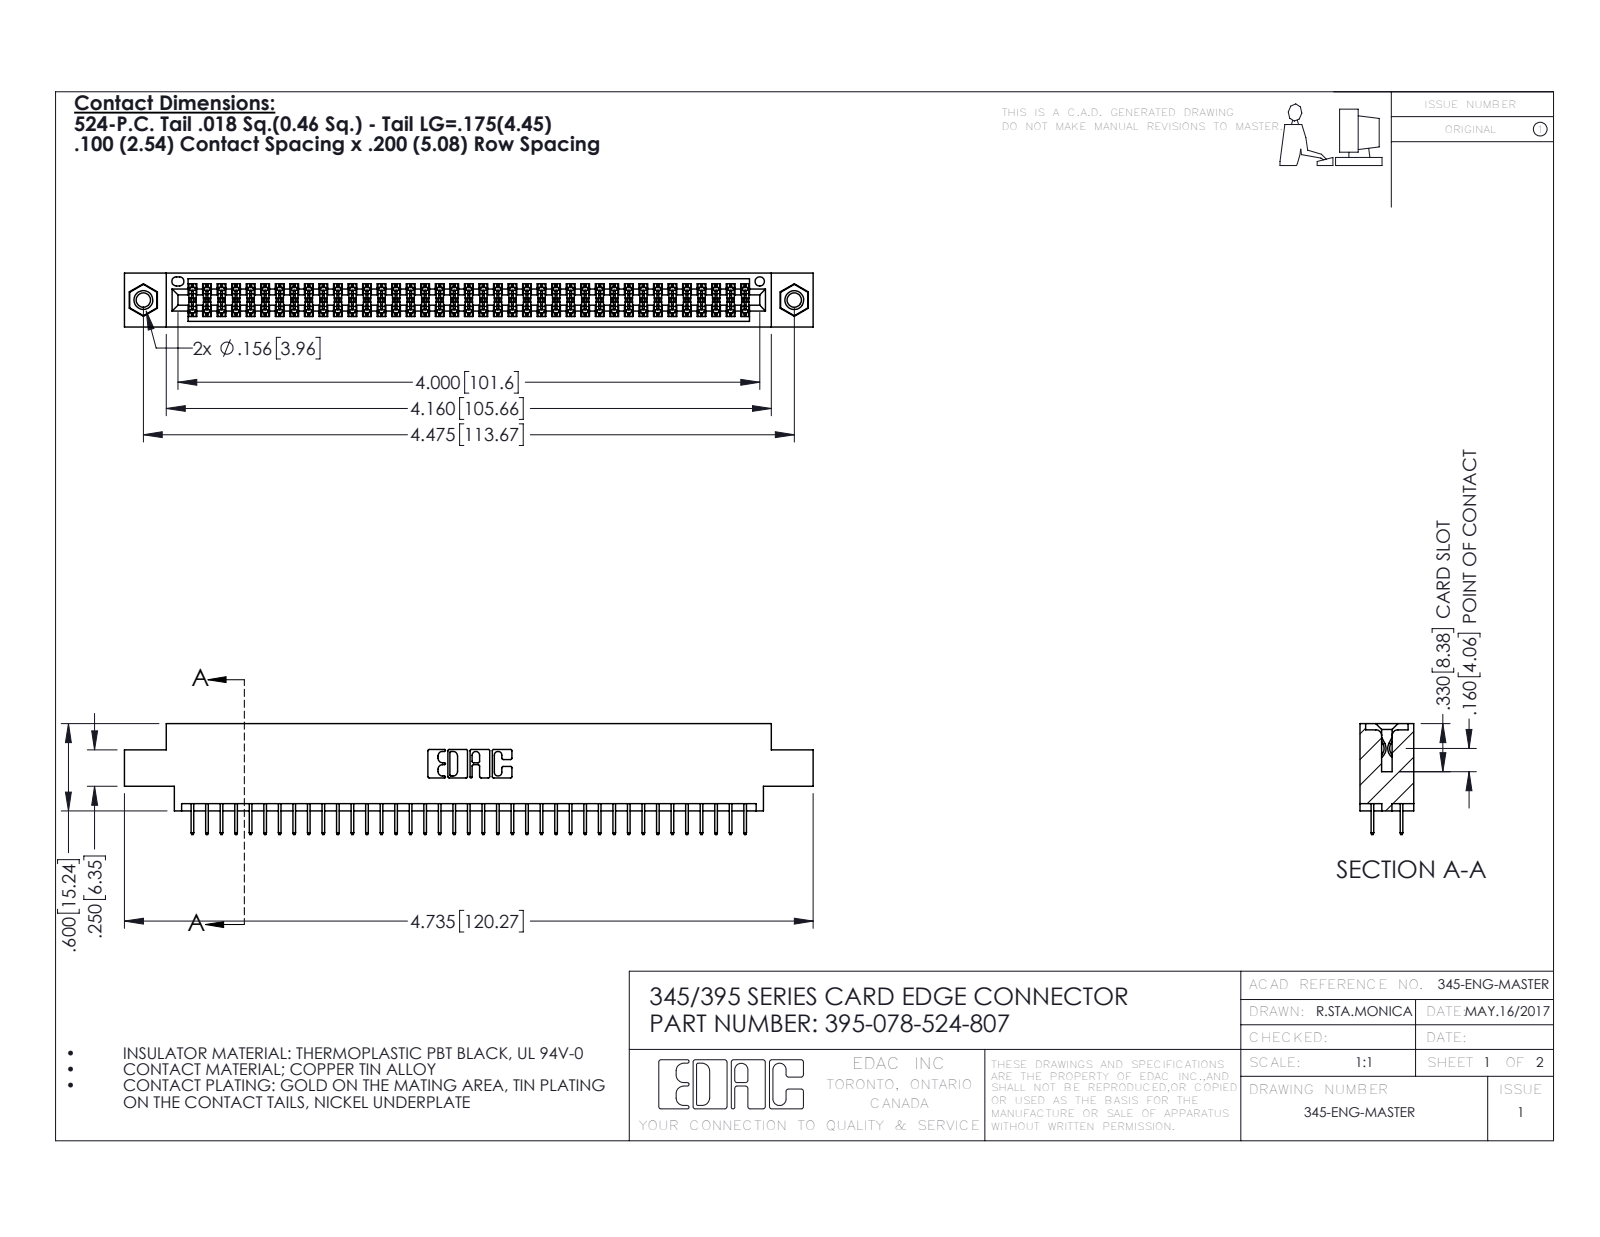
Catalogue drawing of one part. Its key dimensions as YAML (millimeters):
part_name: "345 Part_0.170 Offset - 0.156 Dia-TI; 345-250-001_345-250-005-103; 345-292-001_345-293-124; 395-078-524-807"
step_written_by: "SolidWorks 2016 (CONFIG_CONTROL_DESIGN)"
units: millimeters
bodies: {solids: 81, faces: 4402, planar: 3158, cylindrical: 1228, other: 16}
overall_size: [120.3, 19.4, 9.4]
volume: 11400
surface_area: 16670
round_holes:
  - {diameter: 2.5, count: 2}
  - {diameter: 3.2, count: 2}
  - {diameter: 4, count: 2}
  - {diameter: 1.6, count: 1}
round_bosses_or_shafts:
  - {diameter: 3.9, count: 2}
partial_cylinders:
  - {radius: 0.2, count: 117}
  - {radius: 0.3, count: 22}
  - {radius: 0.2, count: 6}
  - {radius: 0.8, count: 6}
  - {radius: 0.7, count: 3}
  - {radius: 0.4, count: 2}
  - {radius: 0.5, count: 2}
  - {radius: 0.6, count: 2}
face_to_face_distances: [1.8, 7.6, 9.4, 5.1, 2.5, 6.9, 0.6, 5.7, 4.4, 1.8]
hole_center_spacings: [6.9, 107.7, 113.7]
